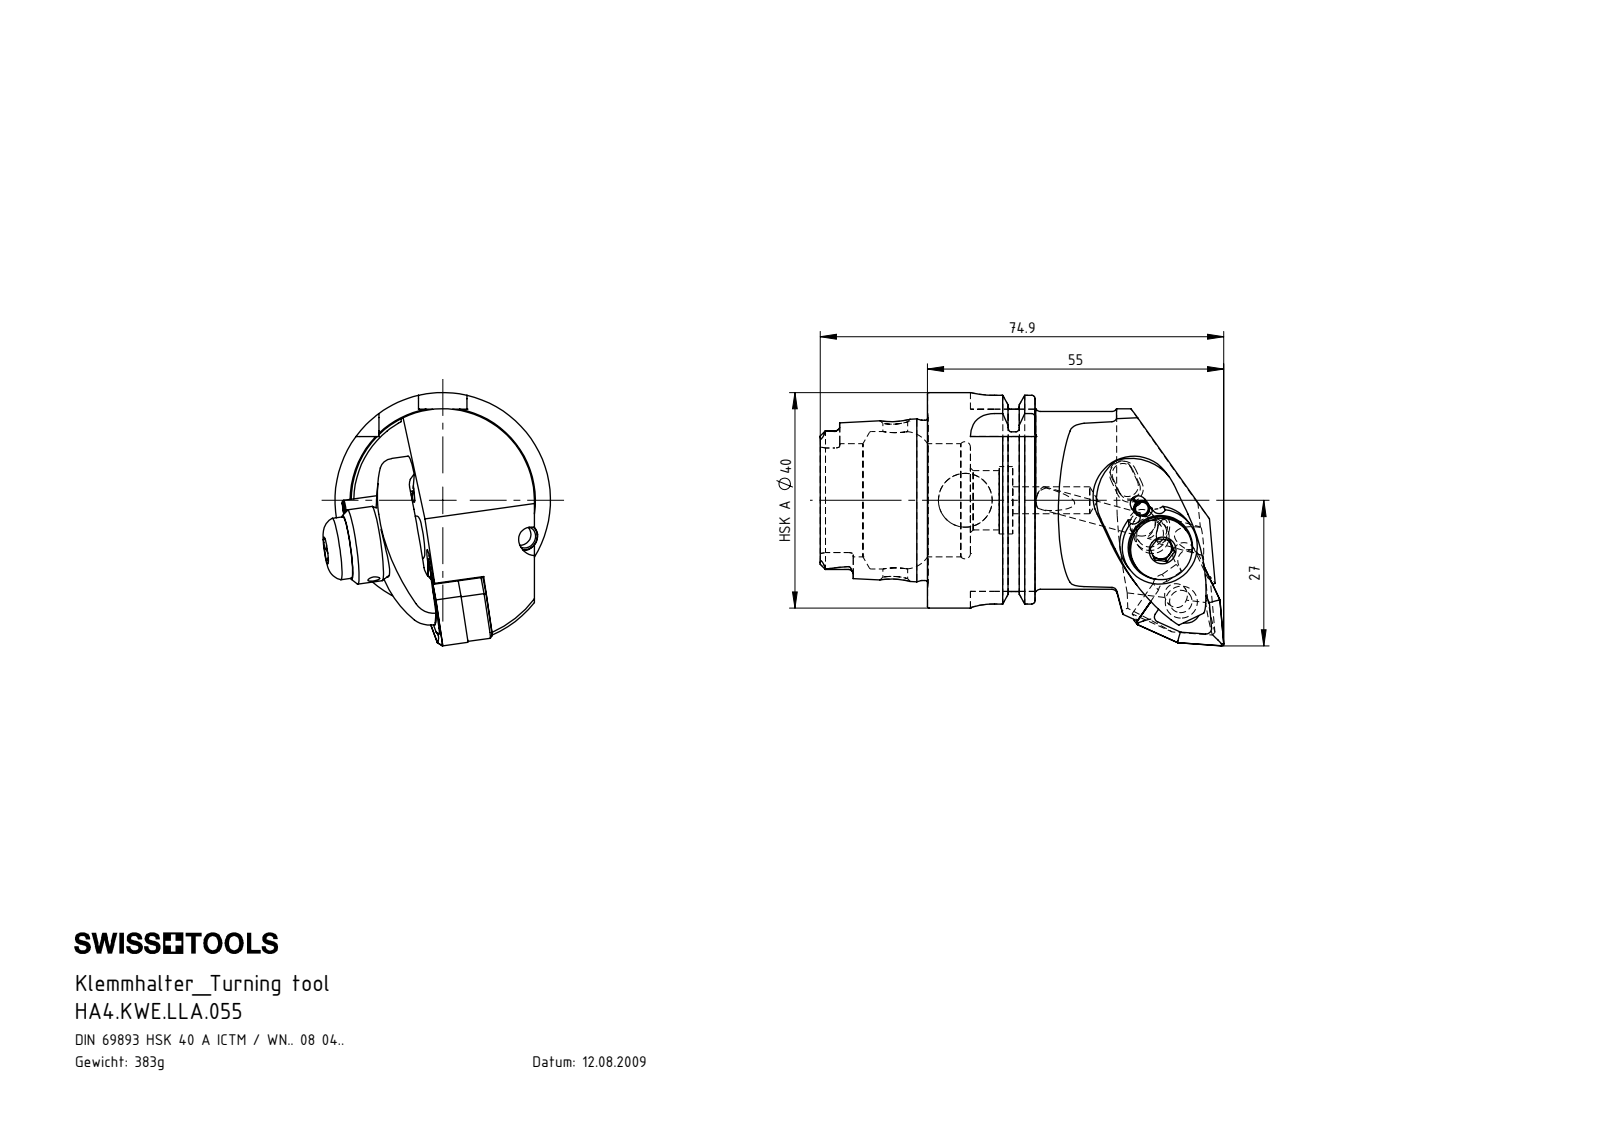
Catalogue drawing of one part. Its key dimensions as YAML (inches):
part_name: "WCC-ER2.001.010_A; HA4.KWE.LLA.055; KVT_MB_600_050; WCC-ER4.103.032_A (+7 more)"
step_written_by: "SolidWorks 2017 (AUTOMOTIVE_DESIGN)"
units: inches
bodies: {solids: 11, faces: 369, planar: 139, cylindrical: 106, other: 124}
overall_size: [2.949, 1.85, 1.662]
volume: 2.943
surface_area: 29.42
round_holes:
  - {diameter: 0.079, count: 3}
  - {diameter: 0.197, count: 3}
  - {diameter: 0.165, count: 2}
  - {diameter: 0.276, count: 2}
  - {diameter: 0.094, count: 1}
  - {diameter: 0.118, count: 1}
  - {diameter: 0.157, count: 1}
  - {diameter: 0.181, count: 1}
  - {diameter: 0.203, count: 1}
  - {diameter: 0.244, count: 1}
  - {diameter: 0.264, count: 1}
  - {diameter: 0.307, count: 1}
round_bosses_or_shafts:
  - {diameter: 0.197, count: 2}
  - {diameter: 0.118, count: 2}
  - {diameter: 1.575, count: 1}
  - {diameter: 1.368, count: 1}
  - {diameter: 1.299, count: 1}
  - {diameter: 1.17, count: 1}
  - {diameter: 0.551, count: 1}
  - {diameter: 0.453, count: 1}
partial_cylinders:
  - {radius: 0.015, count: 6}
  - {radius: 0.035, count: 6}
  - {radius: 0.177, count: 4}
  - {radius: 0.016, count: 3}
  - {radius: 0.027, count: 3}
  - {radius: 0.027, count: 3}
  - {radius: 0.039, count: 3}
  - {radius: 0.059, count: 3}
face_to_face_distances: [0.177, 0.313, 0.228, 0.05, 0.472, 0.785, 0.783, 1.096, 1.569, 0.187]
hole_center_spacings: [0.315, 0.591, 0.906, 0.315, 0.323, 0.323, 0.582, 0.583]
